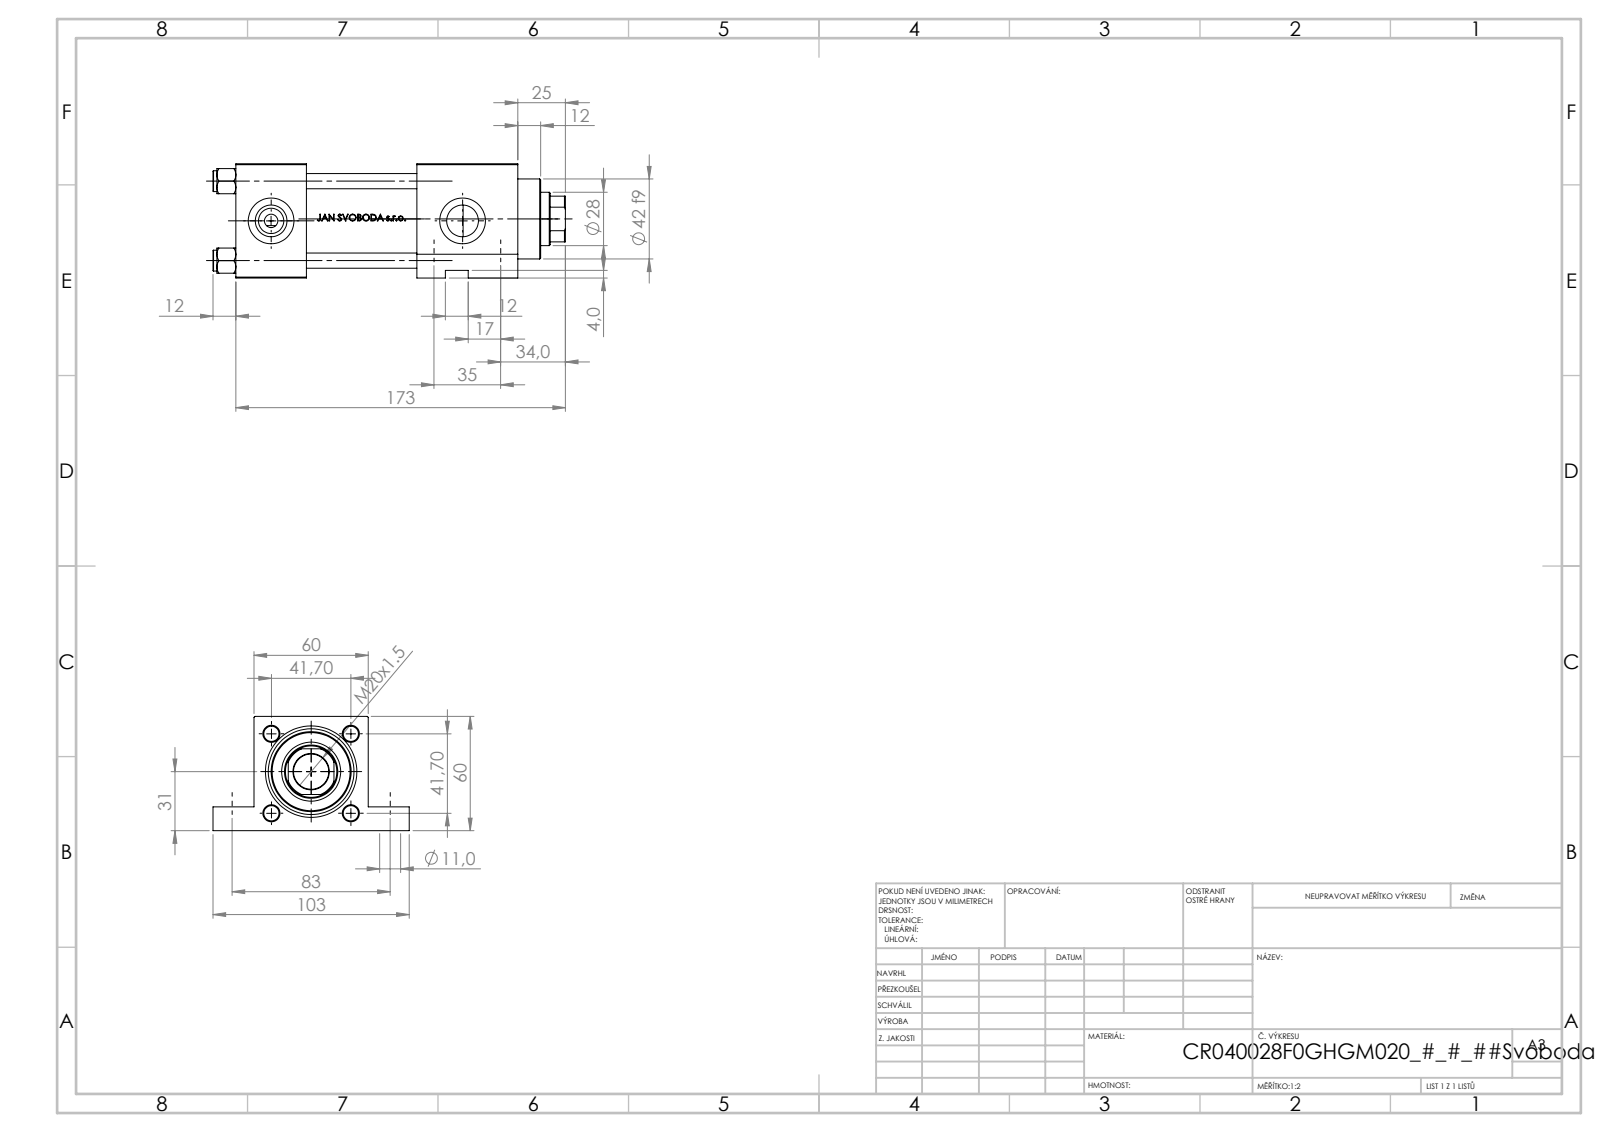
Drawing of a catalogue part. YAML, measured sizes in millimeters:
part_name: "V215CR_F_Body; NUT_M5_F; V215CR_F_TYCINKA; V215_VC_A (+1 more)"
step_written_by: "SolidWorks 2019 (CONFIG_CONTROL_DESIGN)"
units: millimeters
bodies: {solids: 11, faces: 1118, planar: 437, cylindrical: 141, other: 540}
overall_size: [185, 103, 60]
volume: 445246
surface_area: 117639
round_holes:
  - {diameter: 8, count: 4}
  - {diameter: 7, count: 2}
  - {diameter: 11, count: 2}
  - {diameter: 11, count: 2}
  - {diameter: 16.66, count: 2}
  - {diameter: 24, count: 2}
  - {diameter: 18.5, count: 1}
  - {diameter: 28, count: 1}
  - {diameter: 31, count: 1}
  - {diameter: 40, count: 1}
  - {diameter: 45, count: 1}
round_bosses_or_shafts:
  - {diameter: 11, count: 4}
  - {diameter: 46, count: 1}
  - {diameter: 42, count: 1}
partial_cylinders:
  - {radius: 13.5, count: 1}
face_to_face_distances: [60, 37, 95, 58, 148, 111, 53, 12.5, 47.5, 38]
hole_center_spacings: [41.7, 28.79, 30.2, 35, 58.97, 83, 90.08, 100.5]
